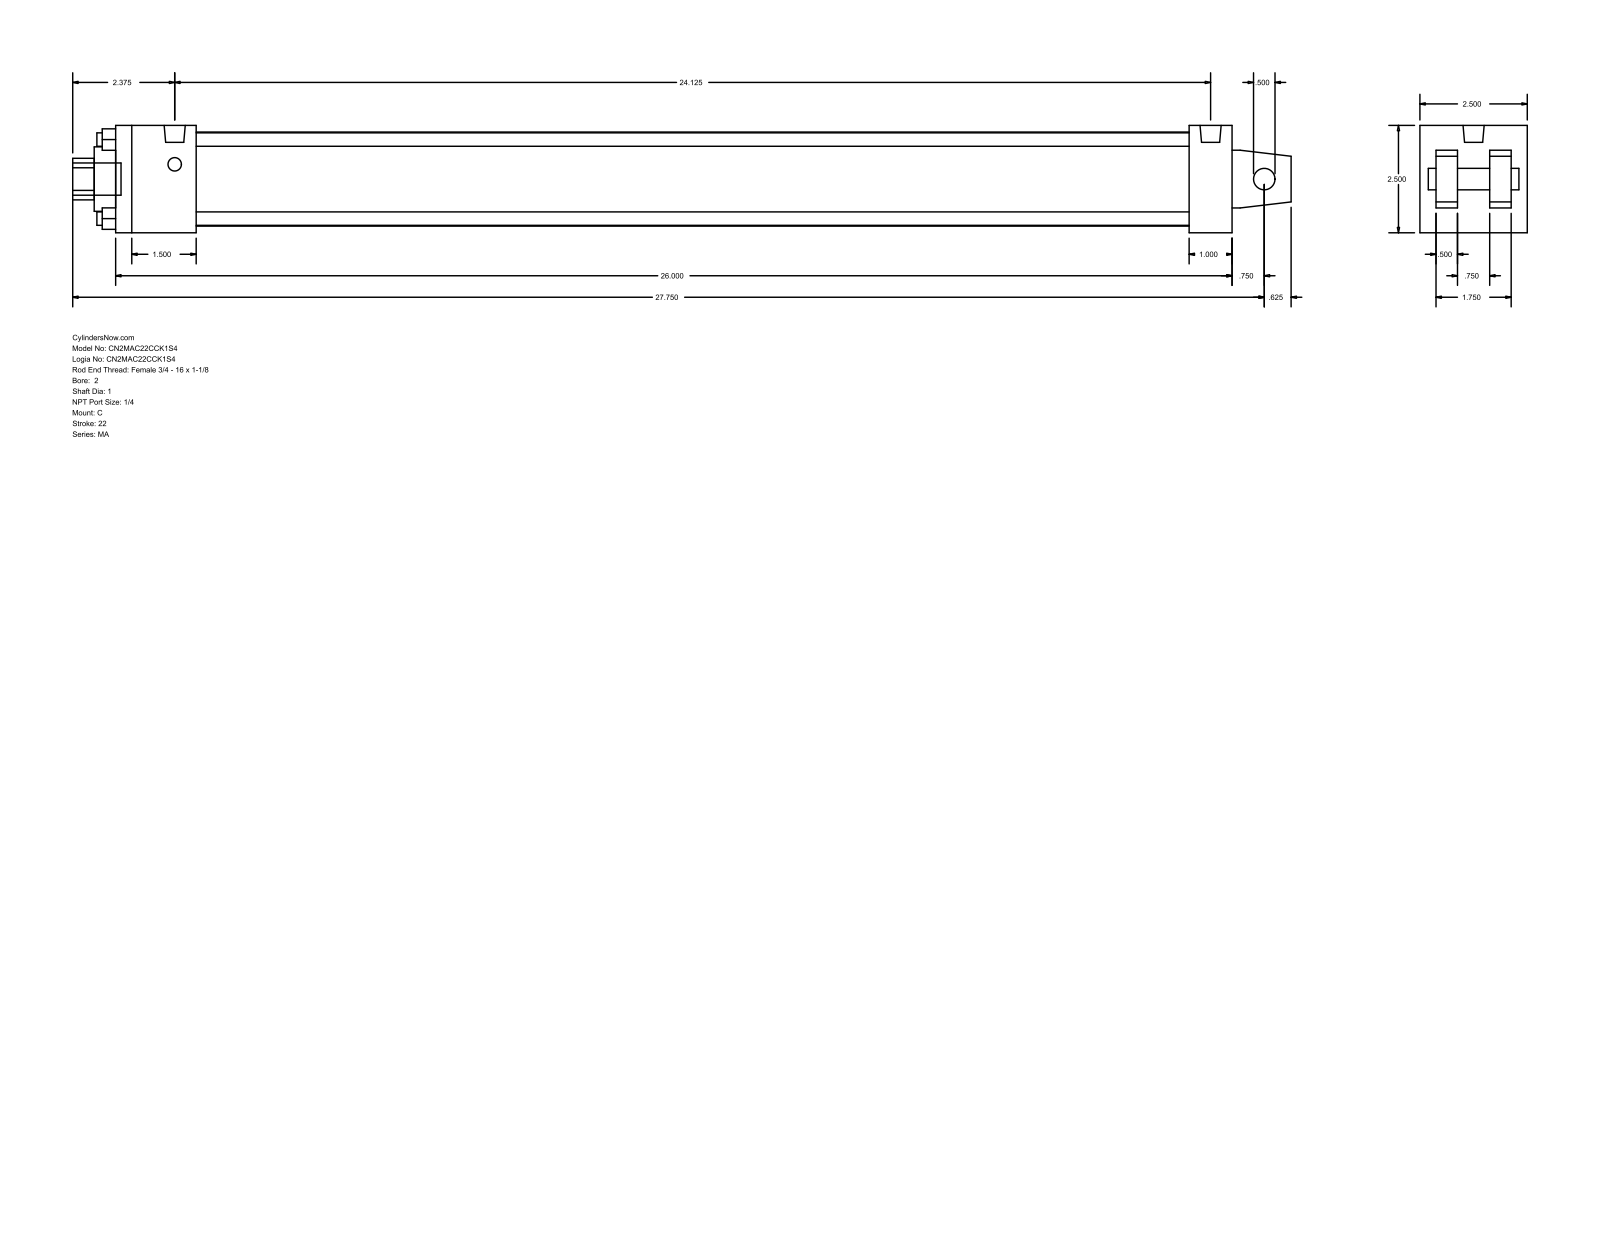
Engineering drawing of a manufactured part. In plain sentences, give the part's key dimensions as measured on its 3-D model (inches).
The part is named "MA_C__0200_1". Its 3-D file was written by "GSSL Pune (CONFIG_CONTROL_DESIGN)". It is 0 solids with 103 faces: 76 planar, 27 cylindrical and 0 other. Overall it measures 28.375 by 2.5 by 2.5 inches. Round holes: 4 of diameter 0.313, 1 of diameter 0.5, 1 of diameter 1, 1 of diameter 1.5, 1 of diameter 2.19. Round bosses or shafts: 4 of diameter 0.313, 2 of diameter 0.492, 1 of diameter 0.75. Partial cylindrical surfaces (rounded edges, fillets, slot ends): 1 of radius 0.484. The main face-to-face distances are 2.5, 0.5, 26, 0.875, 1.625, 0.375, 2.125, 1.25, 1.875, 1. The hole center spacings are 1.301, 1.84, 2.602.
